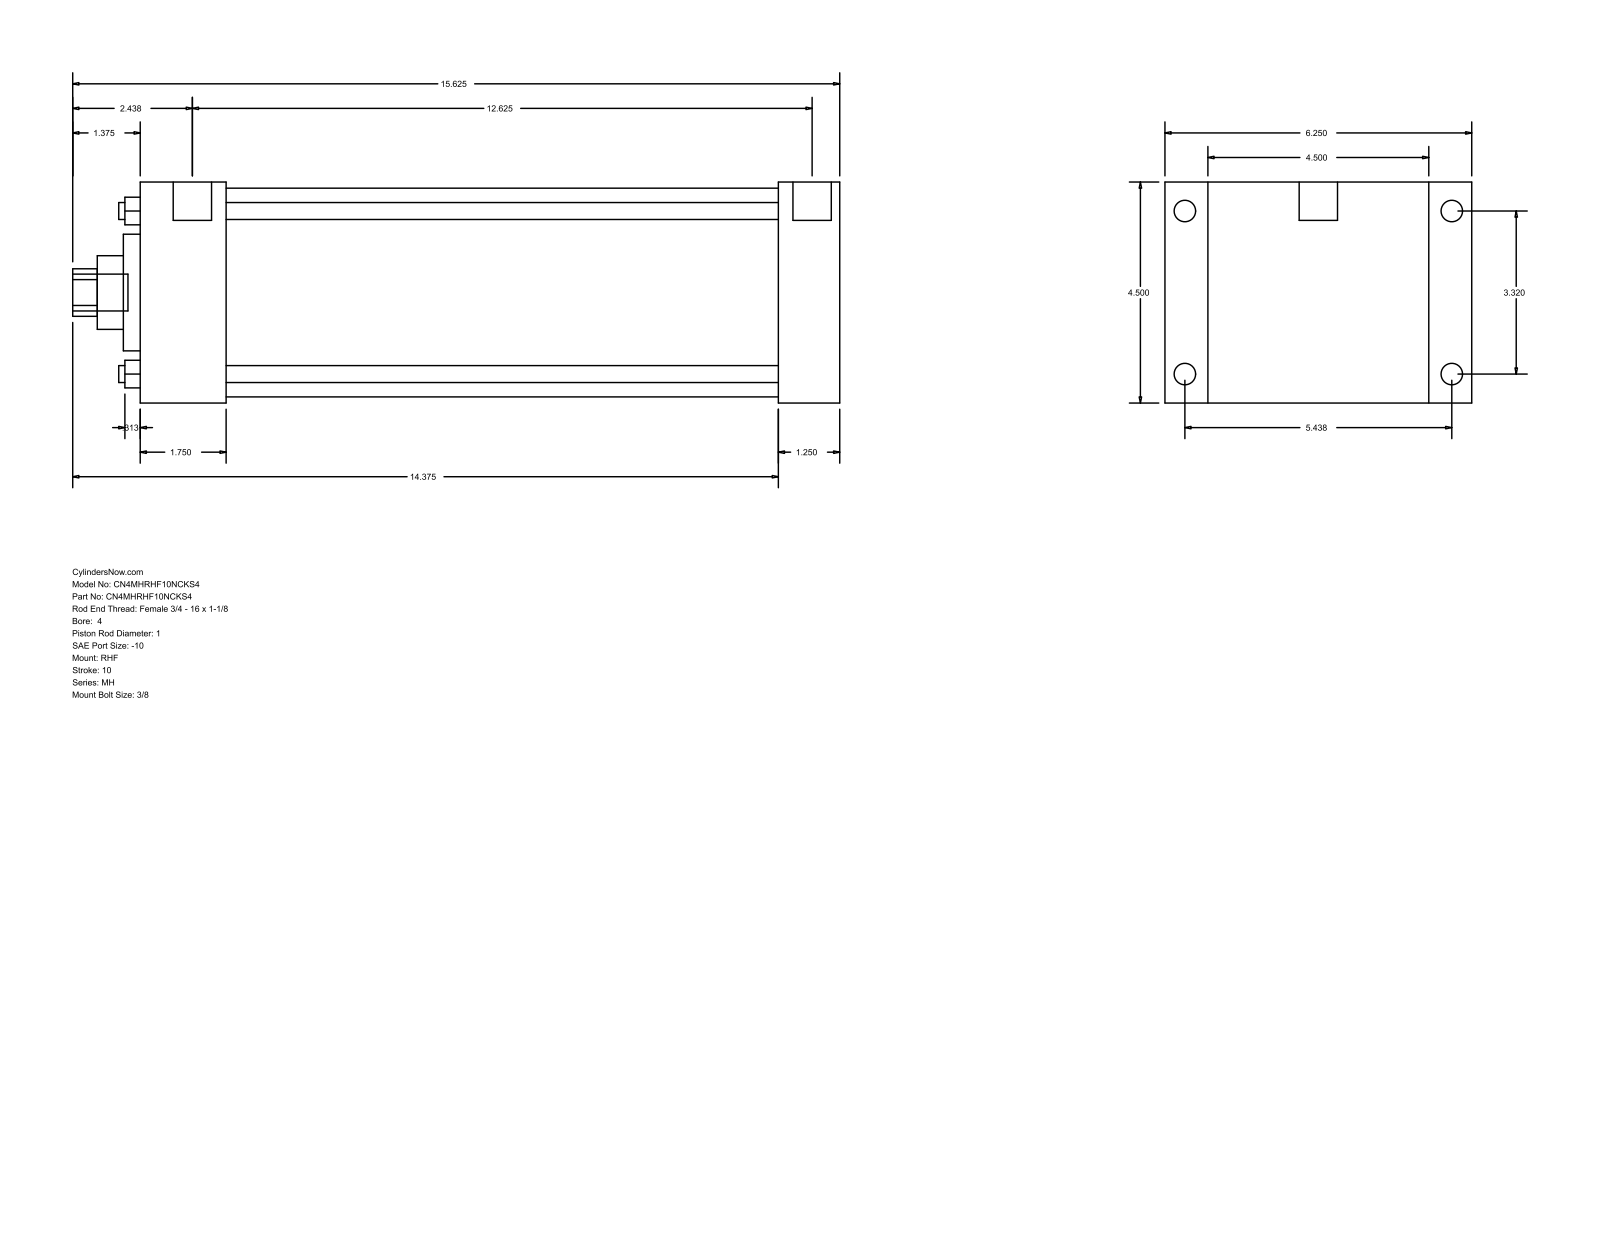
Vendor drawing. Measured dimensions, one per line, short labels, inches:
name: MH_RHF__0400_1
written by: GSSL Pune (CONFIG_CONTROL_DESIGN)
unit: in
bodies: 0 solids, 90 faces (61 planar, 29 cylindrical, 0 other)
size: 15.625 × 6.25 × 4.5
holes: 4× ⌀0.345, 1× ⌀1, 1× ⌀1.5, 1× ⌀2.375, 1× ⌀4.25
bosses: 4× ⌀0.438, 4× ⌀0.344, 2× ⌀0.781, 1× ⌀0.75
rounds: 1× R0.484
face distances: 4.5, 14.25, 13, 1.25, 0.875, 5.375, 1.75, 11.25, 12.5, 6.25
hole spacings: 2.347, 3.32, 4.695
